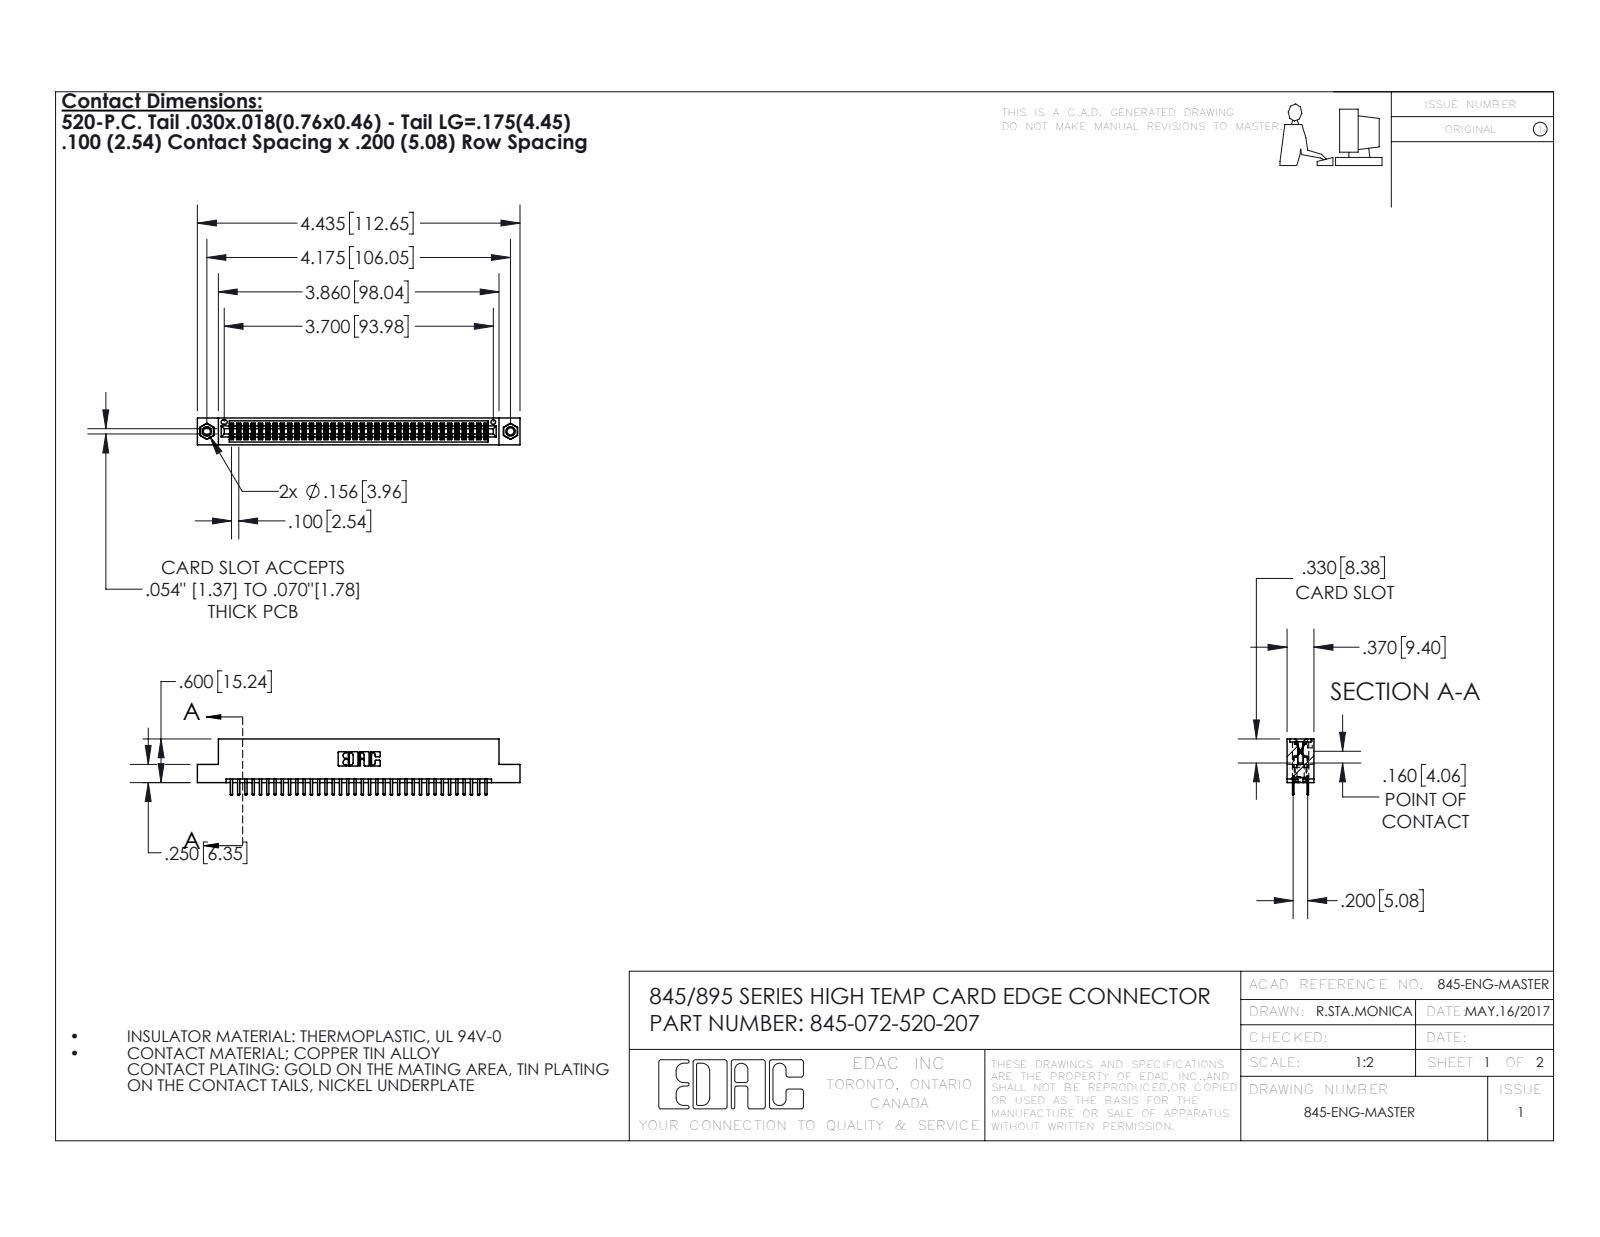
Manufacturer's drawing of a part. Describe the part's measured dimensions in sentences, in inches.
The part is named "345-292-001_345-293-120; 345 Part_Flush Mounting Lugs - 0.156 Dia-TI; 345-250-001_345-250-005-103; 345-072-520-207". Its 3-D file was written by "SolidWorks 2016 (CONFIG_CONTROL_DESIGN)". It is 75 solids with 4074 faces: 2632 planar, 1426 cylindrical and 16 other. Overall it measures 4.435 by 0.775 by 0.37 inches. Its volume is 0.662 cubic inches and its surface area 24.6 square inches. Round holes: 2 of diameter 0.098, 2 of diameter 0.125, 2 of diameter 0.156, 1 of diameter 0.064. Round bosses or shafts: 2 of diameter 0.155. Partial cylindrical surfaces (rounded edges, fillets, slot ends): 108 of radius 0.006, 76 of radius 0.01, 22 of radius 0.01, 6 of radius 0.007, 6 of radius 0.031, 3 of radius 0.026, 2 of radius 0.014, 2 of radius 0.019. The main face-to-face distances are 0.072, 0.298, 0.2, 0.37, 0.098, 0.272, 0.025, 0.225, 0.022, 0.072. The hole center spacings are 0.27, 3.939, 4.175.
